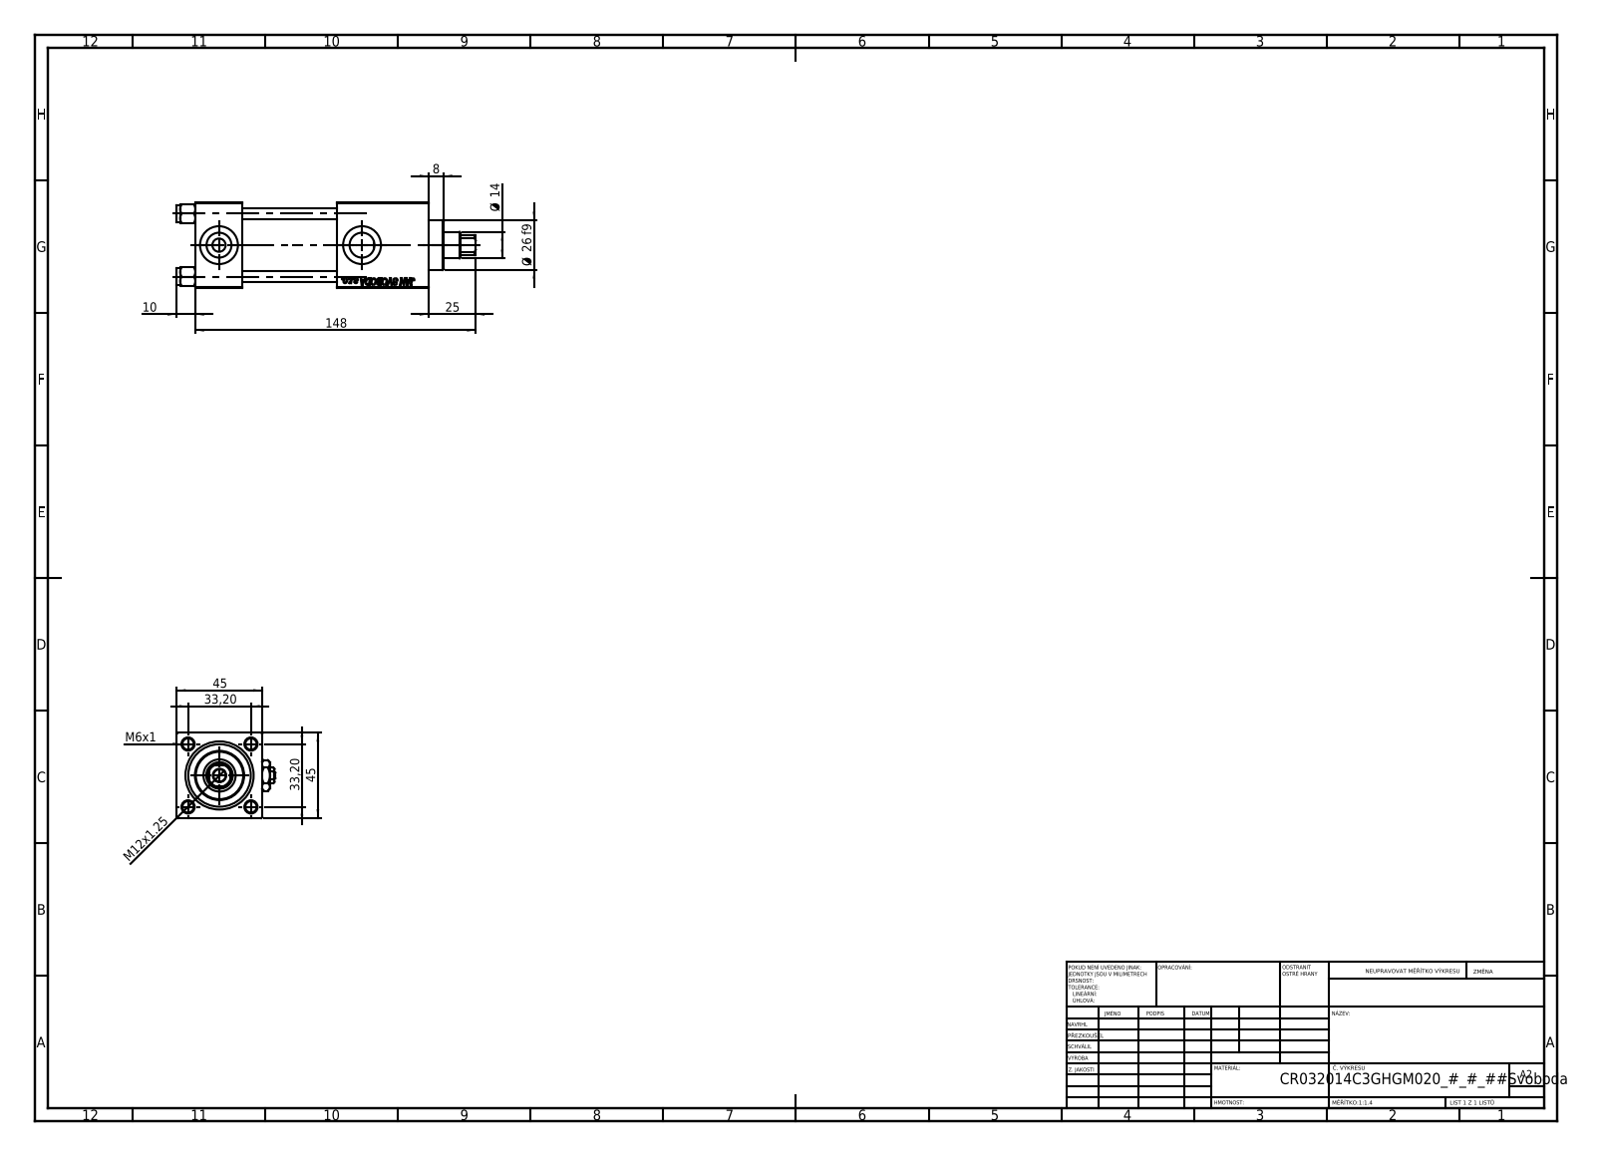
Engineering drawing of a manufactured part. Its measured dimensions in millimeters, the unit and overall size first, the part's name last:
Units: millimetres
Overall size (bounding box): 158 × 52 × 45
Round holes (diameter × count): ⌀6 ×4, ⌀7 ×2, ⌀13.16 ×2, ⌀20 ×2, ⌀6.5 ×1, ⌀14 ×1, ⌀17 ×1, ⌀24 ×1, ⌀32 ×1, ⌀33 ×1
Round bosses / shafts (diameter × count): ⌀9 ×4, ⌀38 ×1, ⌀26 ×1
Partial cylindrical surfaces — rounded edges, fillets, slot ends (radius × count): R6.5 ×1
Main face-to-face distances: 45, 25, 98, 123, 50, 75, 48, 94.3, 69.3, 19.3
Hole centre spacings: 23.48, 33.2, 46.95, 75.5
Volume: 192 342 mm³ · Surface area: 68 925 mm²
Bodies: 13 solids, 1248 faces (572 planar, 98 cylindrical, 578 other)
Part name (STEP PRODUCT): V215CR_C_TYCINKA; NUT_M5_C; V215CR_C_Body; V215_VC_A (+2 more)
STEP written by: SolidWorks 2019 (CONFIG_CONTROL_DESIGN)
